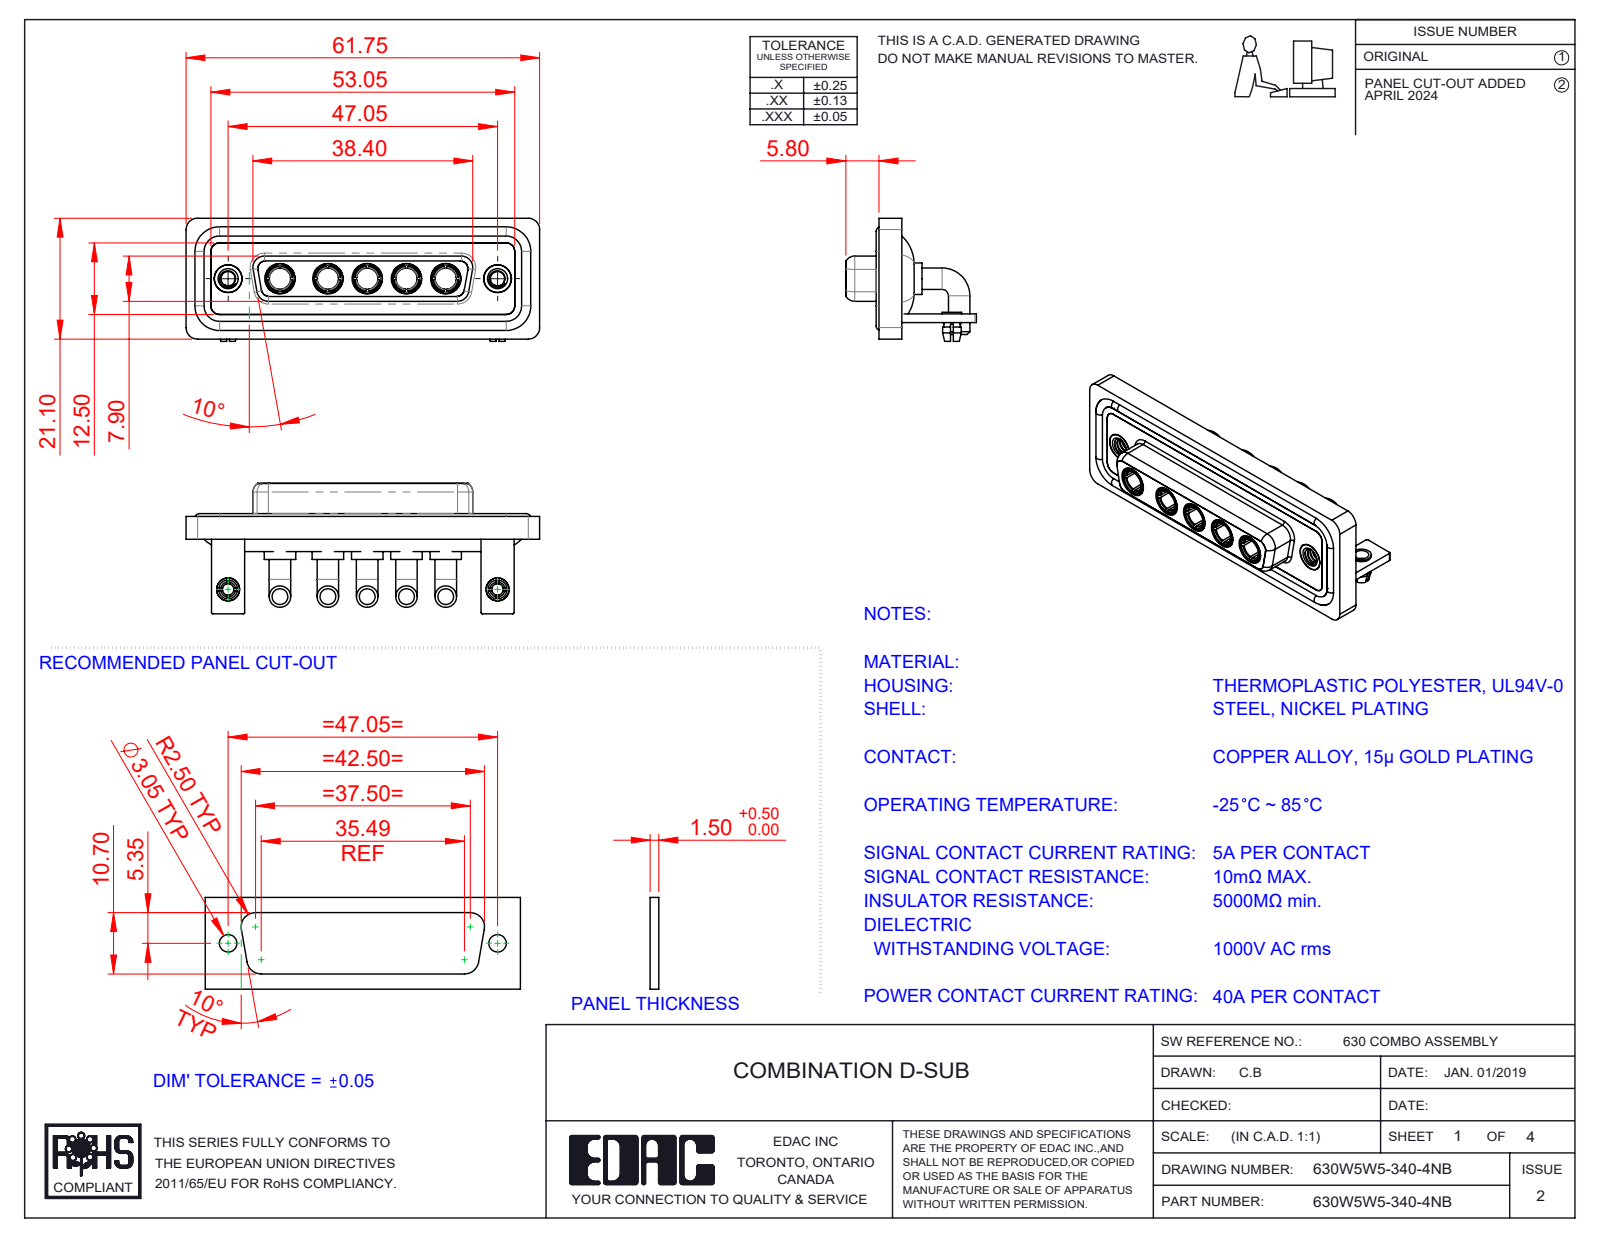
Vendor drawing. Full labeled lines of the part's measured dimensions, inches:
Part name (STEP PRODUCT): 630Combo Board Lock_50 Contacts; 630Combo Threaded Rivet_A; Power Socket_40A RA; 630Combo Housing_5W5 (+5 more)
STEP written by: SolidWorks 2023 (CONFIG_CONTROL_DESIGN)
Units: inches
Bodies: 21 solids, 910 faces (318 planar, 367 cylindrical, 225 other)
Overall size (bounding box): 2.431 × 0.898 × 0.846
Volume: 0.561 in³ · Surface area: 23.22 in²
Round holes (diameter × count): ⌀0.191 ×7, ⌀0.146 ×5, ⌀0.209 ×5, ⌀0.098 ×4, ⌀0.079 ×2, ⌀0.126 ×2, ⌀0.157 ×2, ⌀0.159 ×2, ⌀0.197 ×2
Round bosses / shafts (diameter × count): ⌀0.148 ×10, ⌀0.217 ×5, ⌀0.205 ×5, ⌀0.195 ×5, ⌀0.187 ×5, ⌀0.063 ×4, ⌀0.195 ×2, ⌀0.189 ×2
Partial cylindrical surfaces — rounded edges, fillets, slot ends (radius × count): R0.079 ×19, R0.059 ×18, R0.01 ×16, R0.053 ×8, R0.063 ×8, R0.02 ×5, R0.083 ×5, R0.024 ×4
Main face-to-face distances: 0.016, 0.071, 0.114, 0.146, 0.059, 0.161, 0.043, 0.055, 0.063, 0.098
Hole centre spacings: 0.27, 0.356, 1.496, 1.852, 0.27, 0.33, 0.54, 0.541
